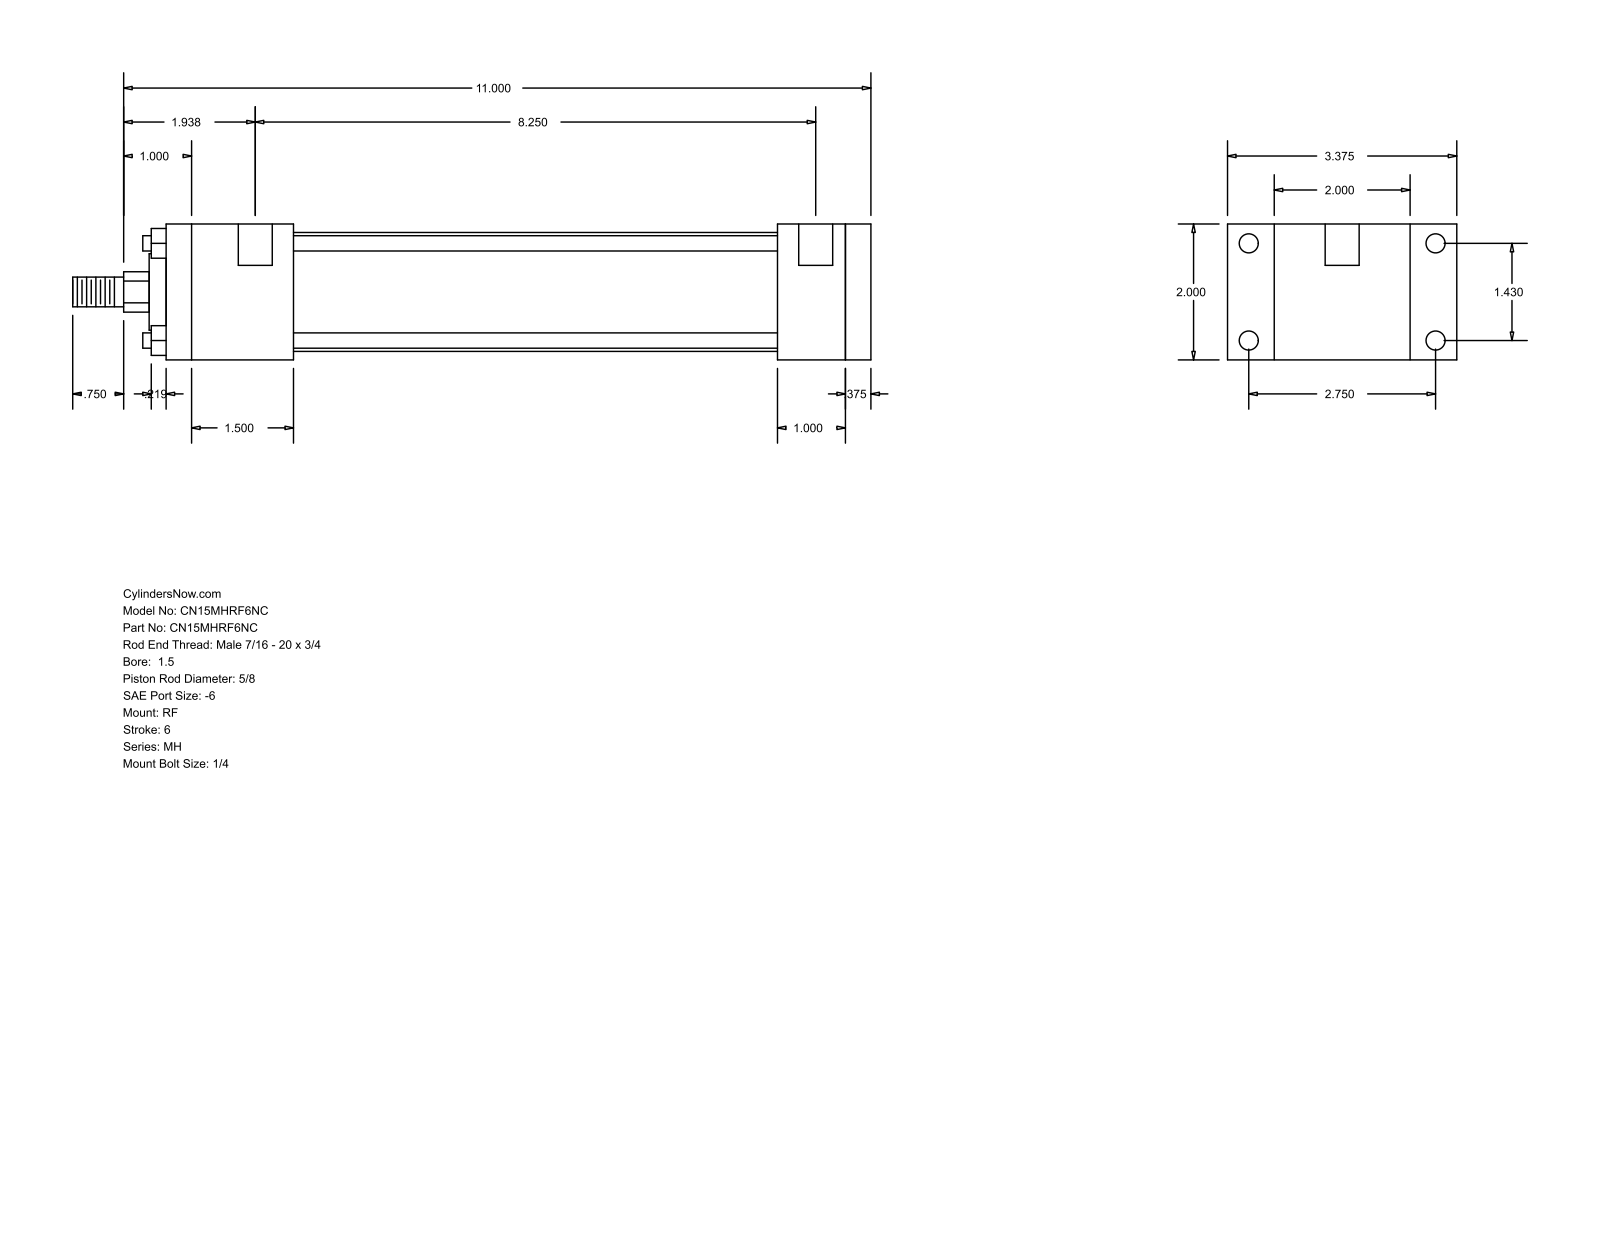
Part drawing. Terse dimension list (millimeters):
name: MH_RF__0150_0.625
written by: GSSL Pune (CONFIG_CONTROL_DESIGN)
unit: mm
bodies: 0 solids, 92 faces (64 planar, 28 cylindrical, 0 other)
size: 298.45 × 85.72 × 50.8
holes: 4× ⌀5.56, 4× ⌀7.14, 2× ⌀12.7
bosses: 4× ⌀5.71, 1× ⌀44.45, 1× ⌀28.57, 1× ⌀15.88, 1× ⌀11.11
rounds: 1× R7.54
face distances: 50.8, 9.52, 263.52, 254, 34.93, 17.46, 68.26, 228.59, 25.41, 47.62
hole spacings: 36.32, 69.84, 78.72, 212.72, 3.17, 209.55
